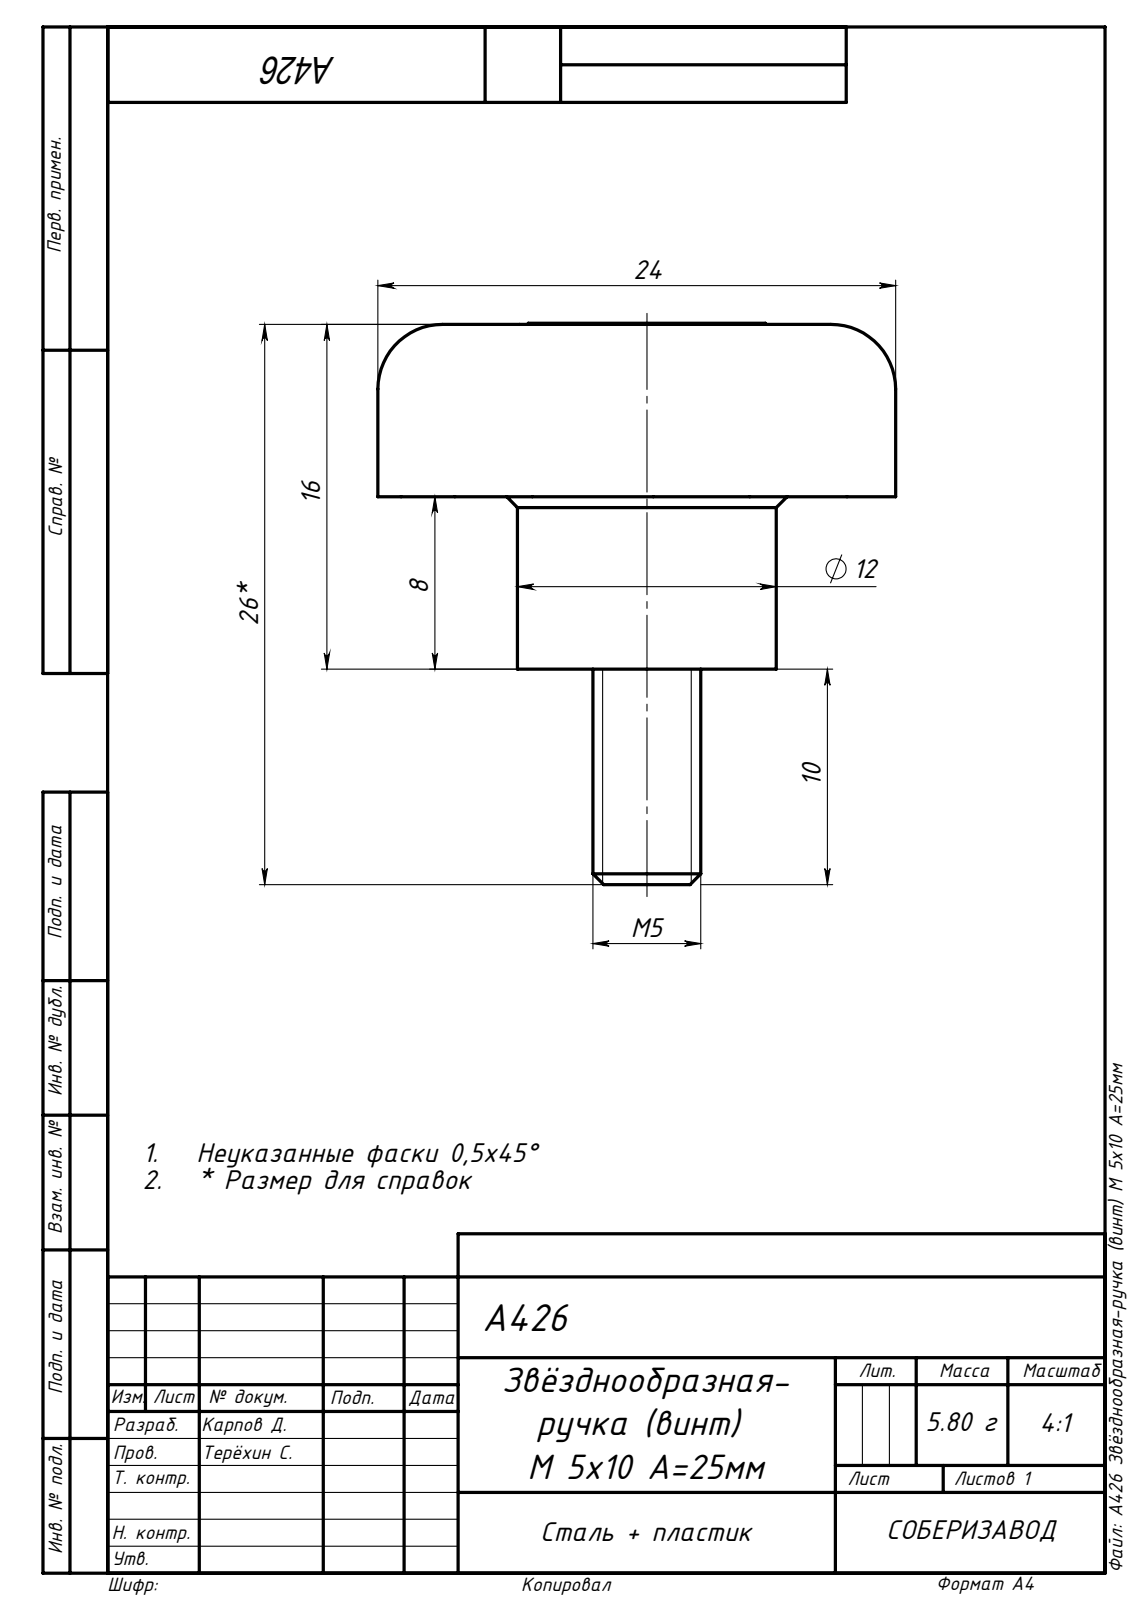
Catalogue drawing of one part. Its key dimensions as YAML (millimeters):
part_name: "A426 Звёзднообразная-ручка (винт) М 5х10 А=25мм"
step_written_by: "SolidWorks 2021 (AUTOMOTIVE_DESIGN)"
units: millimeters
bodies: {solids: 2, faces: 96, planar: 21, cylindrical: 56, other: 19}
overall_size: [26.05, 24.47, 24.01]
volume: 3782
surface_area: 2745
round_bosses_or_shafts:
  - {diameter: 13, count: 1}
  - {diameter: 12, count: 1}
  - {diameter: 11, count: 1}
  - {diameter: 5, count: 1}
partial_cylinders:
  - {radius: 1.5, count: 7}
  - {radius: 3, count: 7}
  - {radius: 7, count: 7}
  - {radius: 8.5, count: 7}
  - {radius: 2, count: 6}
face_to_face_distances: [8, 3, 9, 5, 8.05, 5.05, 11, 16, 16.05, 10]
